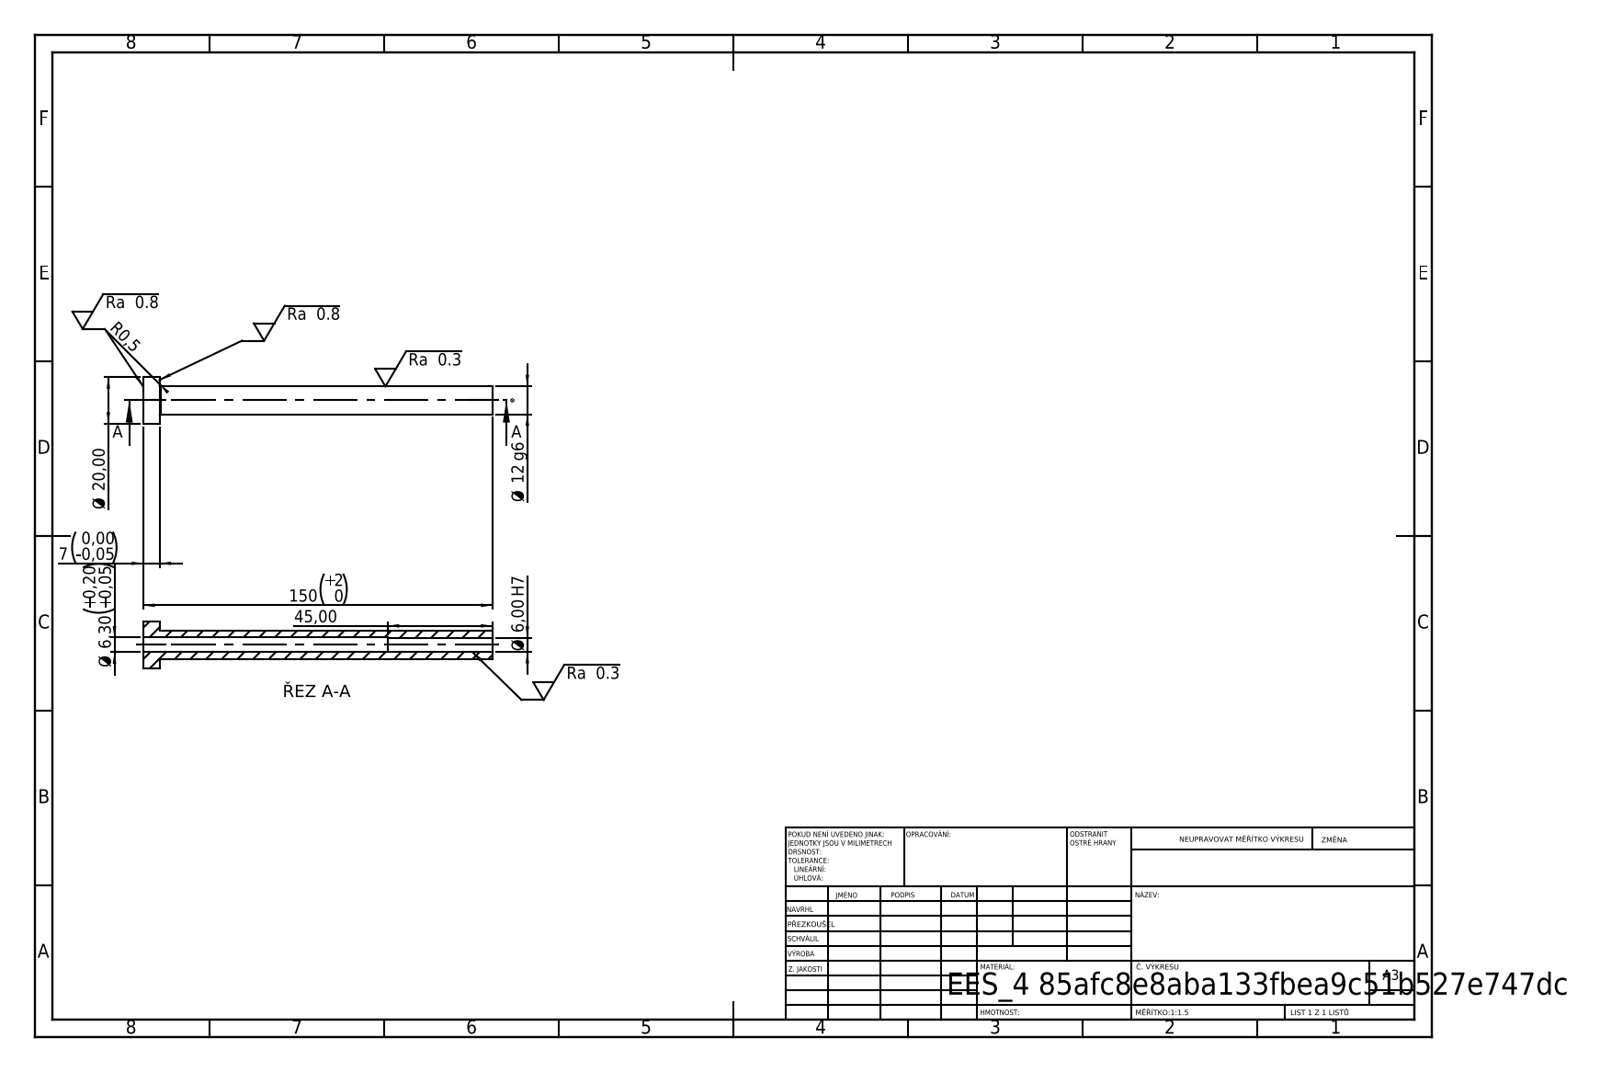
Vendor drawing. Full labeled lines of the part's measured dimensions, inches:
STEP written by: SolidWorks 2019 (CONFIG_CONTROL_DESIGN)
Units: inches
Bodies: 1 solid, 14 faces (4 planar, 8 cylindrical, 2 other)
Overall size (bounding box): 5.906 × 0.787 × 0.787
Volume: 0.844 in³ · Surface area: 14.45 in²
Round holes (diameter × count): ⌀0.236 ×1, ⌀0.248 ×1
Round bosses / shafts (diameter × count): ⌀0.787 ×1, ⌀0.472 ×1
Main face-to-face distances: 0.276, 5.906, 5.63, 4.134, 3.858, 1.772
